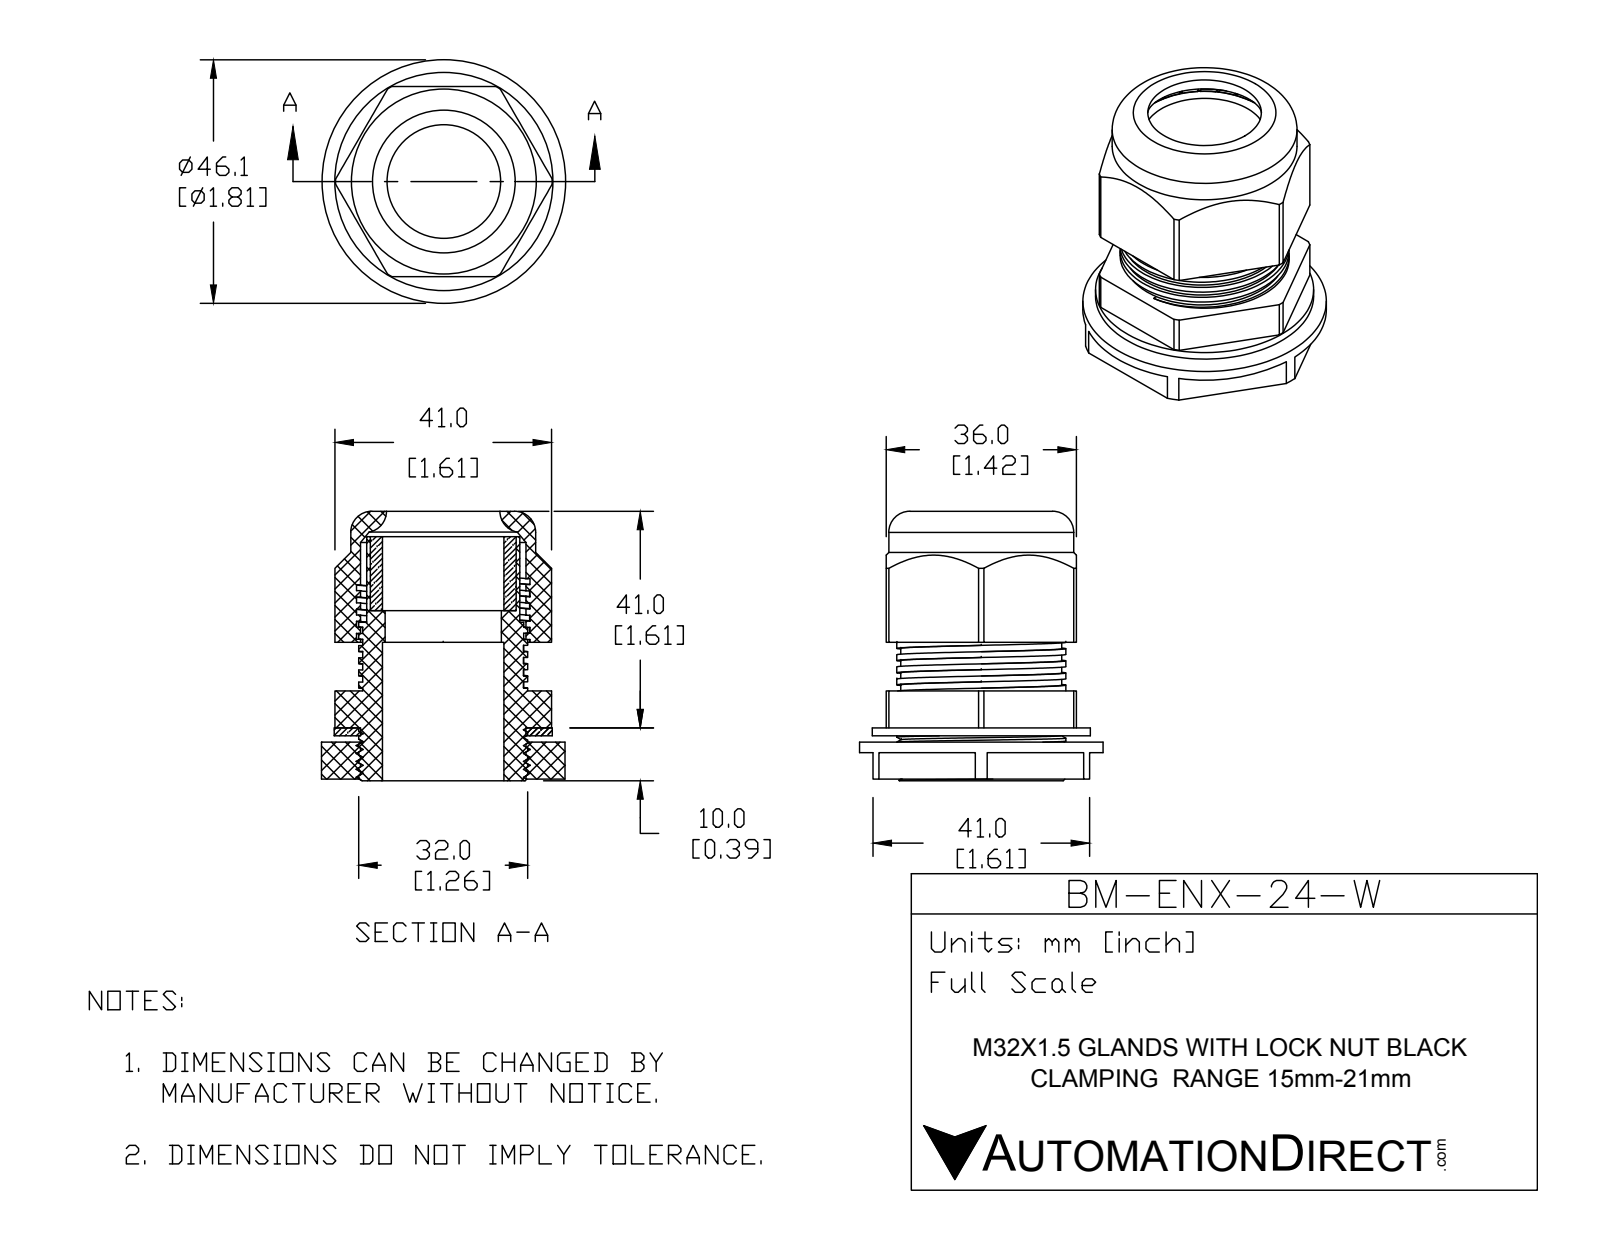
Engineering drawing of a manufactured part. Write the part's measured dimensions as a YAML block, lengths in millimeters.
part_name: "BM-ENX-24-W"
step_written_by: "SolidWorks 2015 (CONFIG_CONTROL_DESIGN)"
units: millimeters
bodies: {solids: 5, faces: 247, planar: 140, cylindrical: 86, other: 21}
overall_size: [51, 46.1, 46.1]
volume: 31002
surface_area: 26357
round_holes:
  - {diameter: 22, count: 1}
  - {diameter: 23, count: 1}
  - {diameter: 27.6, count: 1}
  - {diameter: 31.3, count: 1}
  - {diameter: 31.33, count: 1}
round_bosses_or_shafts:
  - {diameter: 46.1, count: 1}
  - {diameter: 41.3, count: 1}
  - {diameter: 35, count: 1}
  - {diameter: 32, count: 1}
  - {diameter: 29, count: 1}
partial_cylinders:
  - {radius: 20.5, count: 1}
face_to_face_distances: [2.5, 36, 7, 9.5, 8.5, 38.5, 8, 1, 1.5, 0.5]
